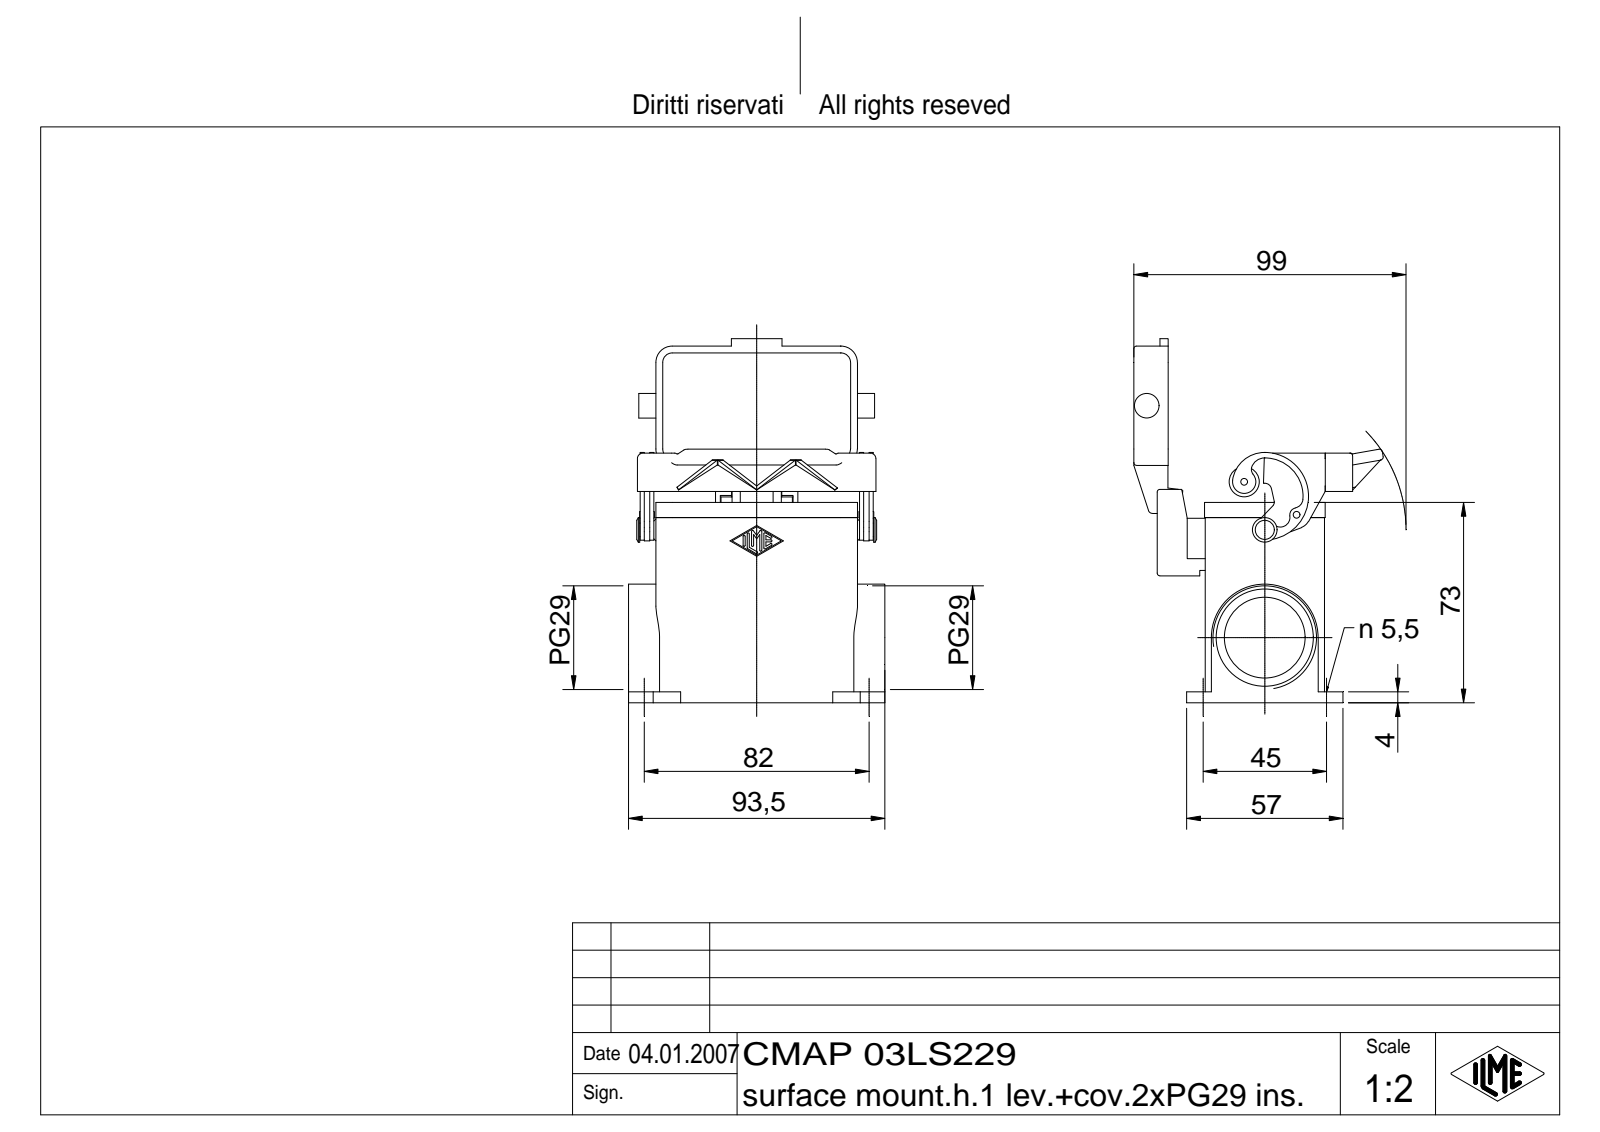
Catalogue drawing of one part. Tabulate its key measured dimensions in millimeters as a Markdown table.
| quantity | value |
| --- | --- |
| part name | CMAP 03LS229 |
| STEP written by | Autodesk Inventor 7 (AUTOMOTIVE_DESIGN) |
| units | millimeters |
| bodies | 6 solids, 594 faces (252 planar, 182 cylindrical, 160 other) |
| overall size | 132.7 × 93.5 × 90.95 |
| volume | 125 169 mm³ |
| surface area | 70 868 mm² |
| round holes (diameter × count) | 5.5 × 4, 2 × 1, 4 × 1, 29.48 × 1, 35.48 × 1 |
| round bosses / shafts (diameter × count) | 9 × 2, 5 × 2, 11 × 1, 7 × 1, 4 × 1, 3 × 1, 2.5 × 1 |
| partial cylindrical surfaces (radius × count) | 1 × 18, 0.38 × 14, 2 × 12, 6 × 12, 1.5 × 6, 3.5 × 6, 3 × 4, 0.5 × 3 |
| main face-to-face distances | 3, 40.5, 4, 43.5, 26, 37.5, 66.5, 69.5, 29, 66 |
| hole center spacings | 45, 82, 93.54, 46.24 |
